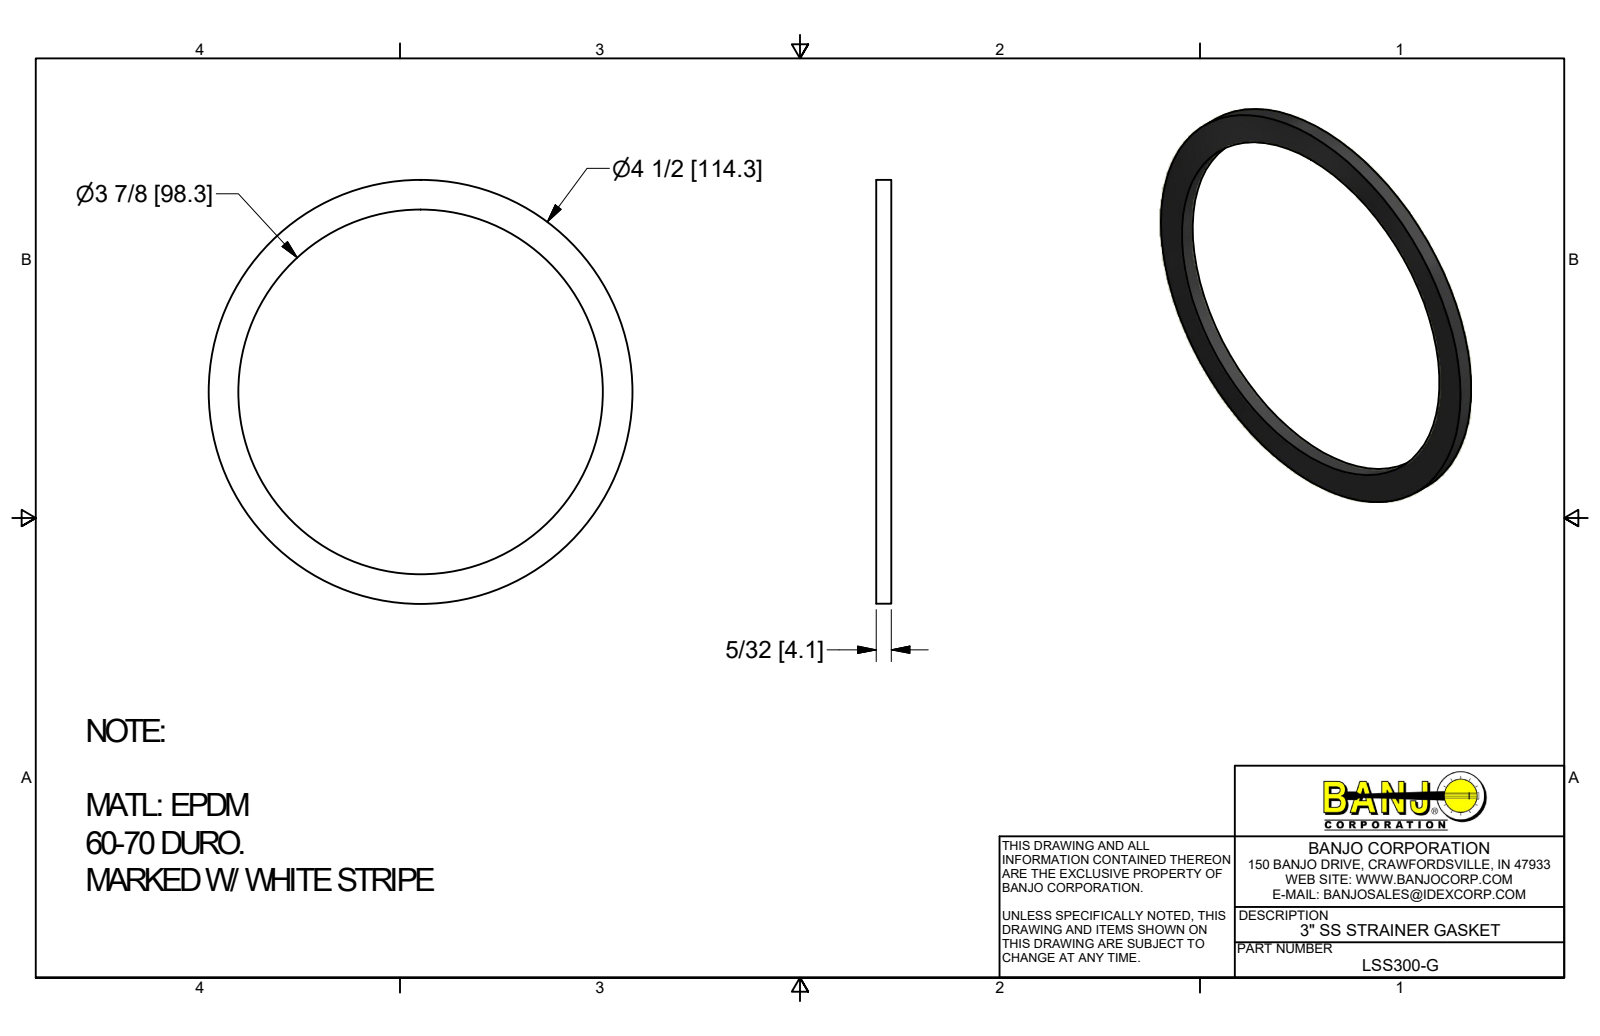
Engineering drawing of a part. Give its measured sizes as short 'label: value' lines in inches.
name: LSS300-G
written by: Autodesk Inventor 2017 (AUTOMOTIVE_DESIGN)
unit: in
bodies: 1 solid, 4 faces (2 planar, 2 cylindrical, 0 other)
size: 4.5 × 4.5 × 0.16
volume: 0.663 in³; area: 12.49 in²
holes: 1× ⌀3.87
bosses: 1× ⌀4.5
face distances: 0.16
